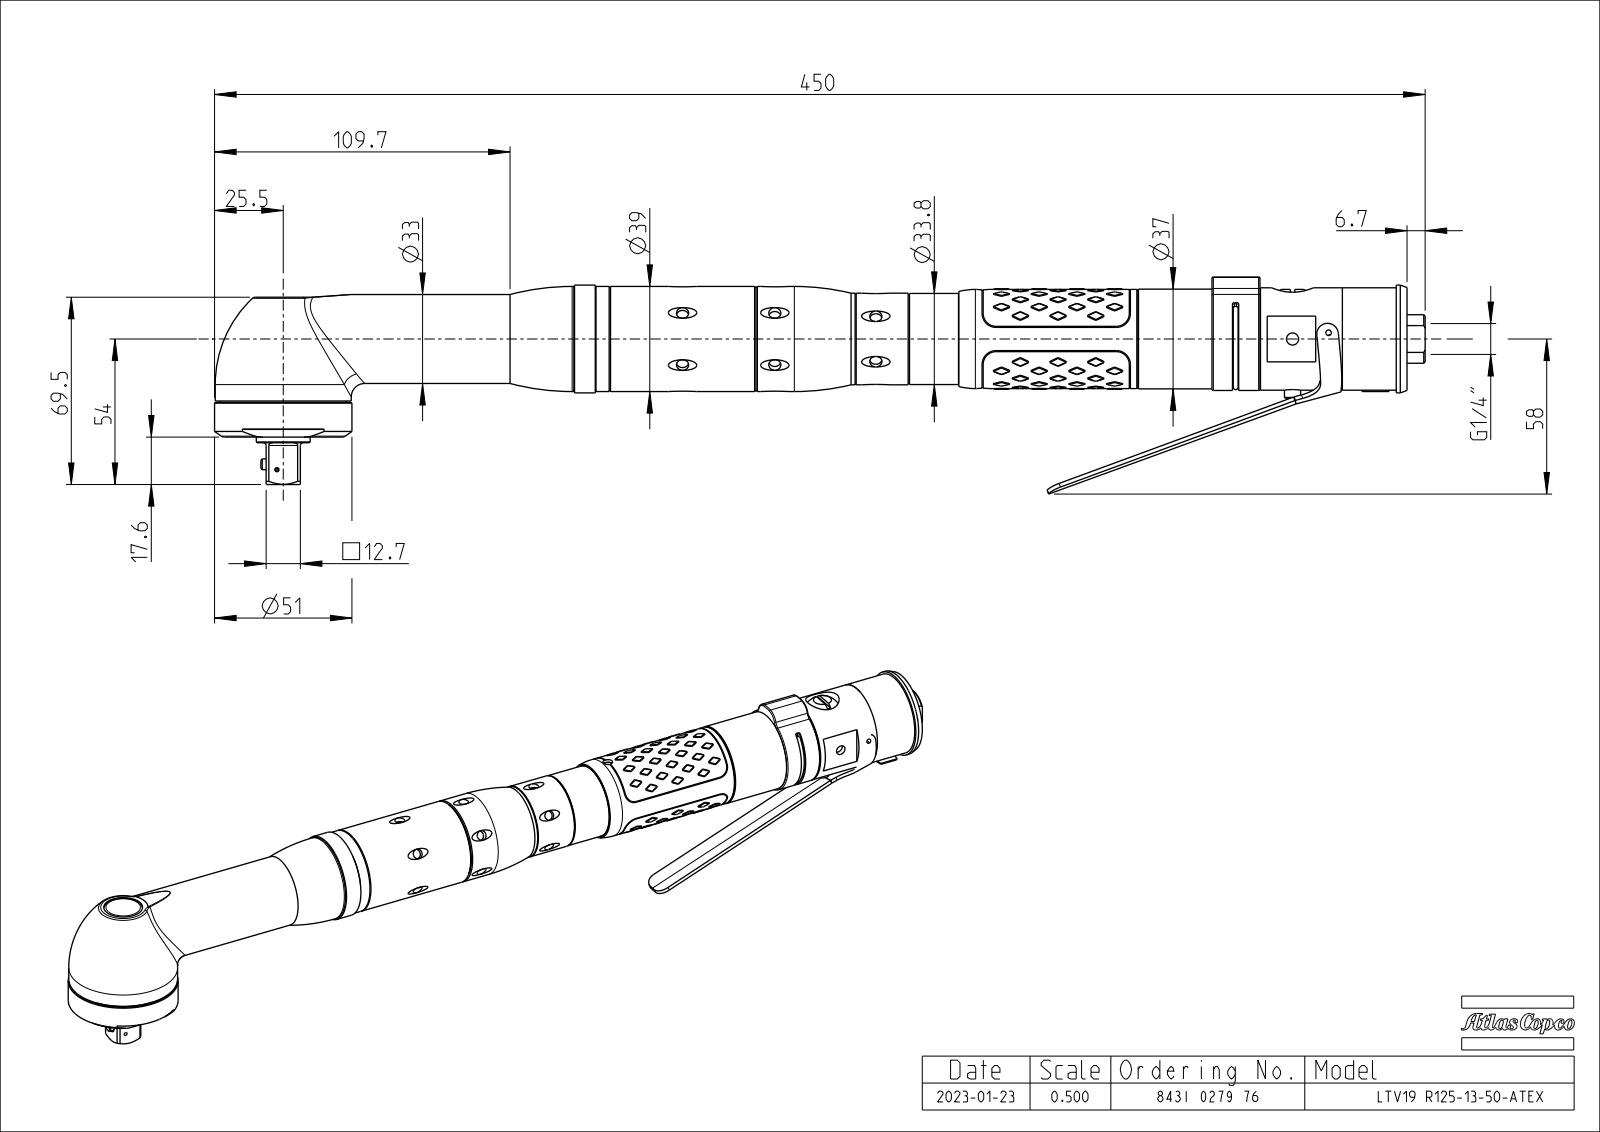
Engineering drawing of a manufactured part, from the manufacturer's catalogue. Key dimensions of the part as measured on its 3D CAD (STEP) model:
Part name (STEP PRODUCT): EXT_COMP_SW0003
STEP written by: CREO PARAMETRIC BY PTC INC, 2020281 (CONFIG_CONTROL_DESIGN)
Units: inches
Bodies: 4 solids, 1322 faces (105 planar, 281 cylindrical, 936 other)
Overall size (bounding box): 17.694 × 3.171 × 2.008
Volume: 31.01 in³ · Surface area: 118.9 in²
Round holes (diameter × count): ⌀0.118 ×12, ⌀0.177 ×11, ⌀0.059 ×1, ⌀0.063 ×1, ⌀0.122 ×1, ⌀0.161 ×1, ⌀0.451 ×1, ⌀0.61 ×1, ⌀0.728 ×1, ⌀0.791 ×1, ⌀1.264 ×1, ⌀1.457 ×1
Round bosses / shafts (diameter × count): ⌀2.008 ×1, ⌀1.988 ×1, ⌀1.89 ×1, ⌀1.843 ×1, ⌀1.575 ×1, ⌀1.535 ×1, ⌀1.504 ×1, ⌀1.496 ×1
Partial cylindrical surfaces — rounded edges, fillets, slot ends (radius × count): R0.02 ×7, R0.008 ×6, R0.031 ×6, R0.039 ×6, R0.028 ×2, R0.045 ×2, R0.059 ×2, R0.157 ×2
Main face-to-face distances: 0.02, 0.079, 0.075, 0.154, 7.291, 7.272, 0.374, 0.157, 2.043, 0.138
Hole centre spacings: 0.63, 0.891, 1.217, 0.326, 1.091, 0.326, 1.091, 1.26
